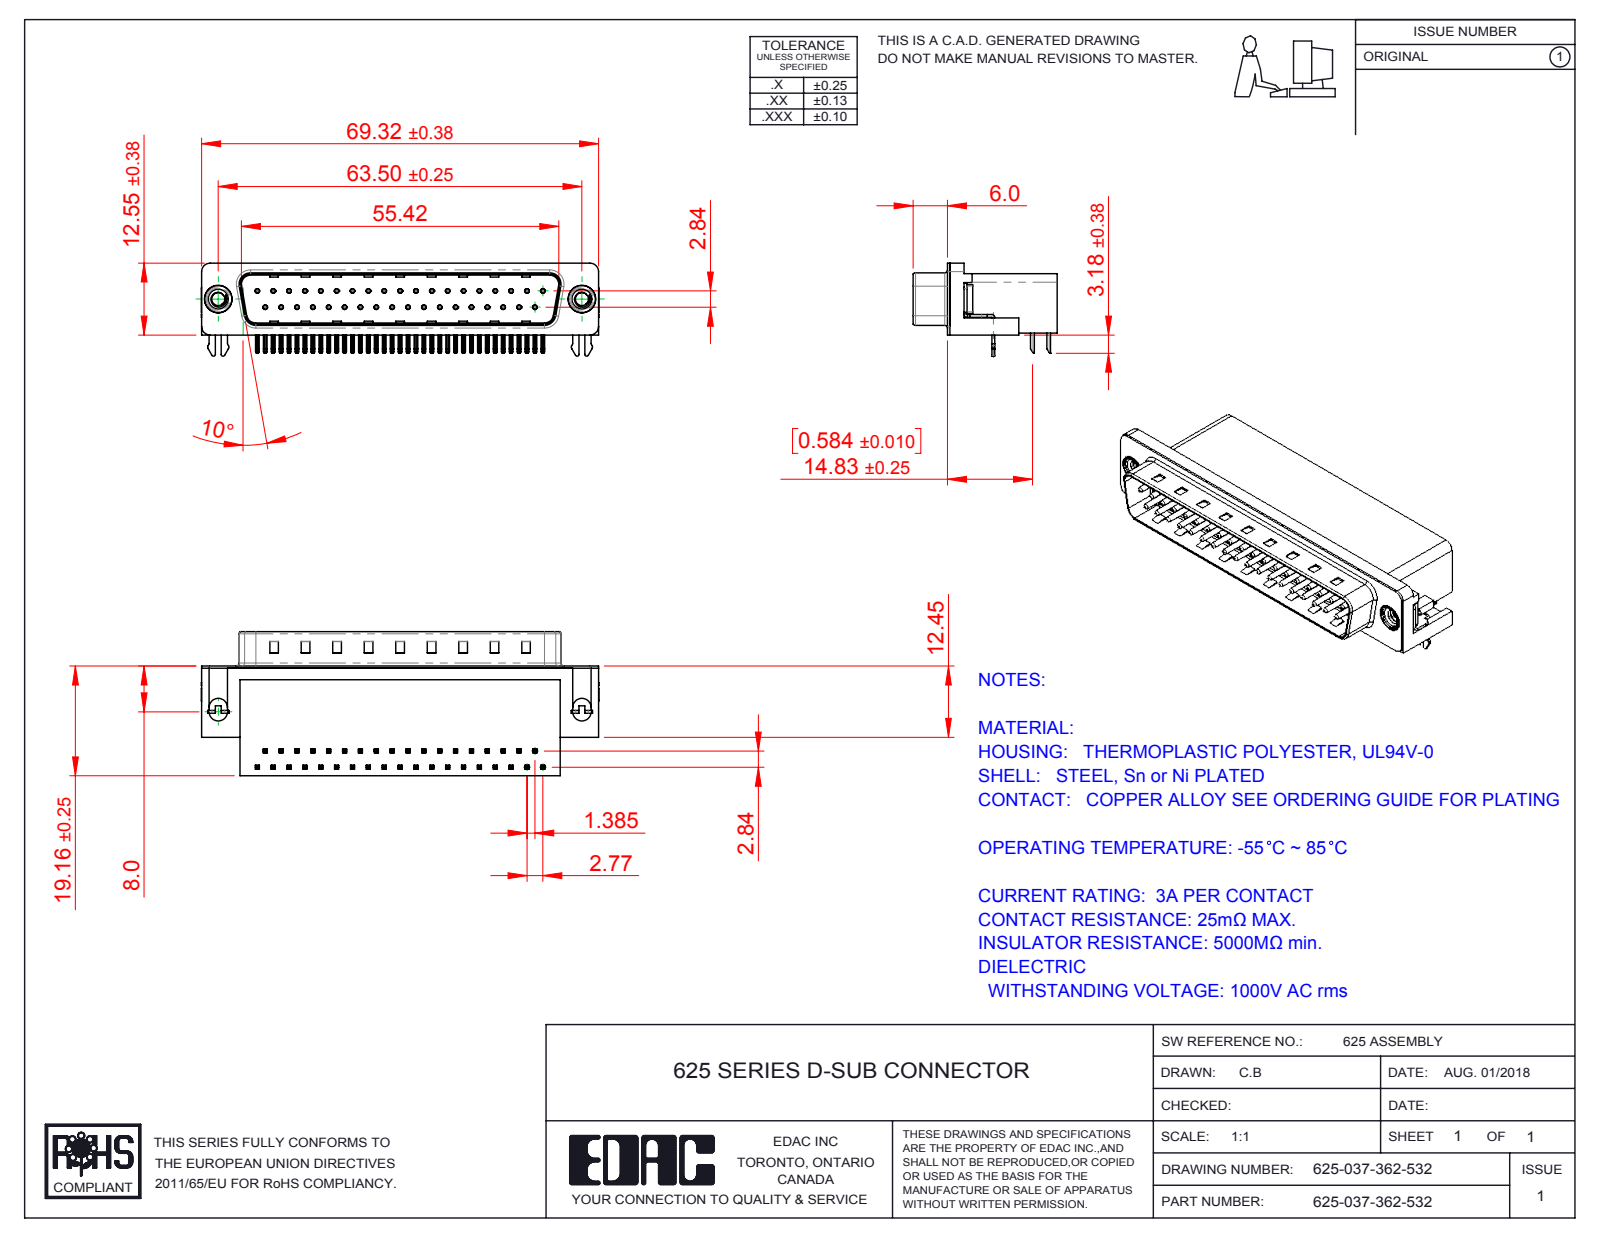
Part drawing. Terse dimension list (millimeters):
name: 625 Contact Bottom; 625-037-362-532; 625 Housing_37 Socket; 625 Contact Top (+3 more)
written by: SolidWorks 2016 (CONFIG_CONTROL_DESIGN)
unit: mm
bodies: 43 solids, 3241 faces (2045 planar, 925 cylindrical, 271 other)
size: 69.4 × 25.16 × 16.25
volume: 12 601 mm³; area: 11 760 mm²
holes: 37× ⌀0.35, 37× ⌀0.8, 2× ⌀2.26, 2× ⌀4, 2× ⌀4.8, 2× ⌀5
bosses: 37× ⌀0.75, 2× ⌀4.9, 2× ⌀4.75, 2× ⌀3.9
rounds: 156× R0.25, 74× R0.12, 16× R1, 14× R0.5, 8× R1.6, 7× R1.5, 4× R0.32, 4× R0.9
face distances: 10.34, 0.4, 18.76, 8.76, 19.16, 2.84, 2.09, 10.1, 1.74, 8.36
hole spacings: 3.16, 2.77, 5.54, 8.31, 11.08, 13.85, 19.39, 22.16
